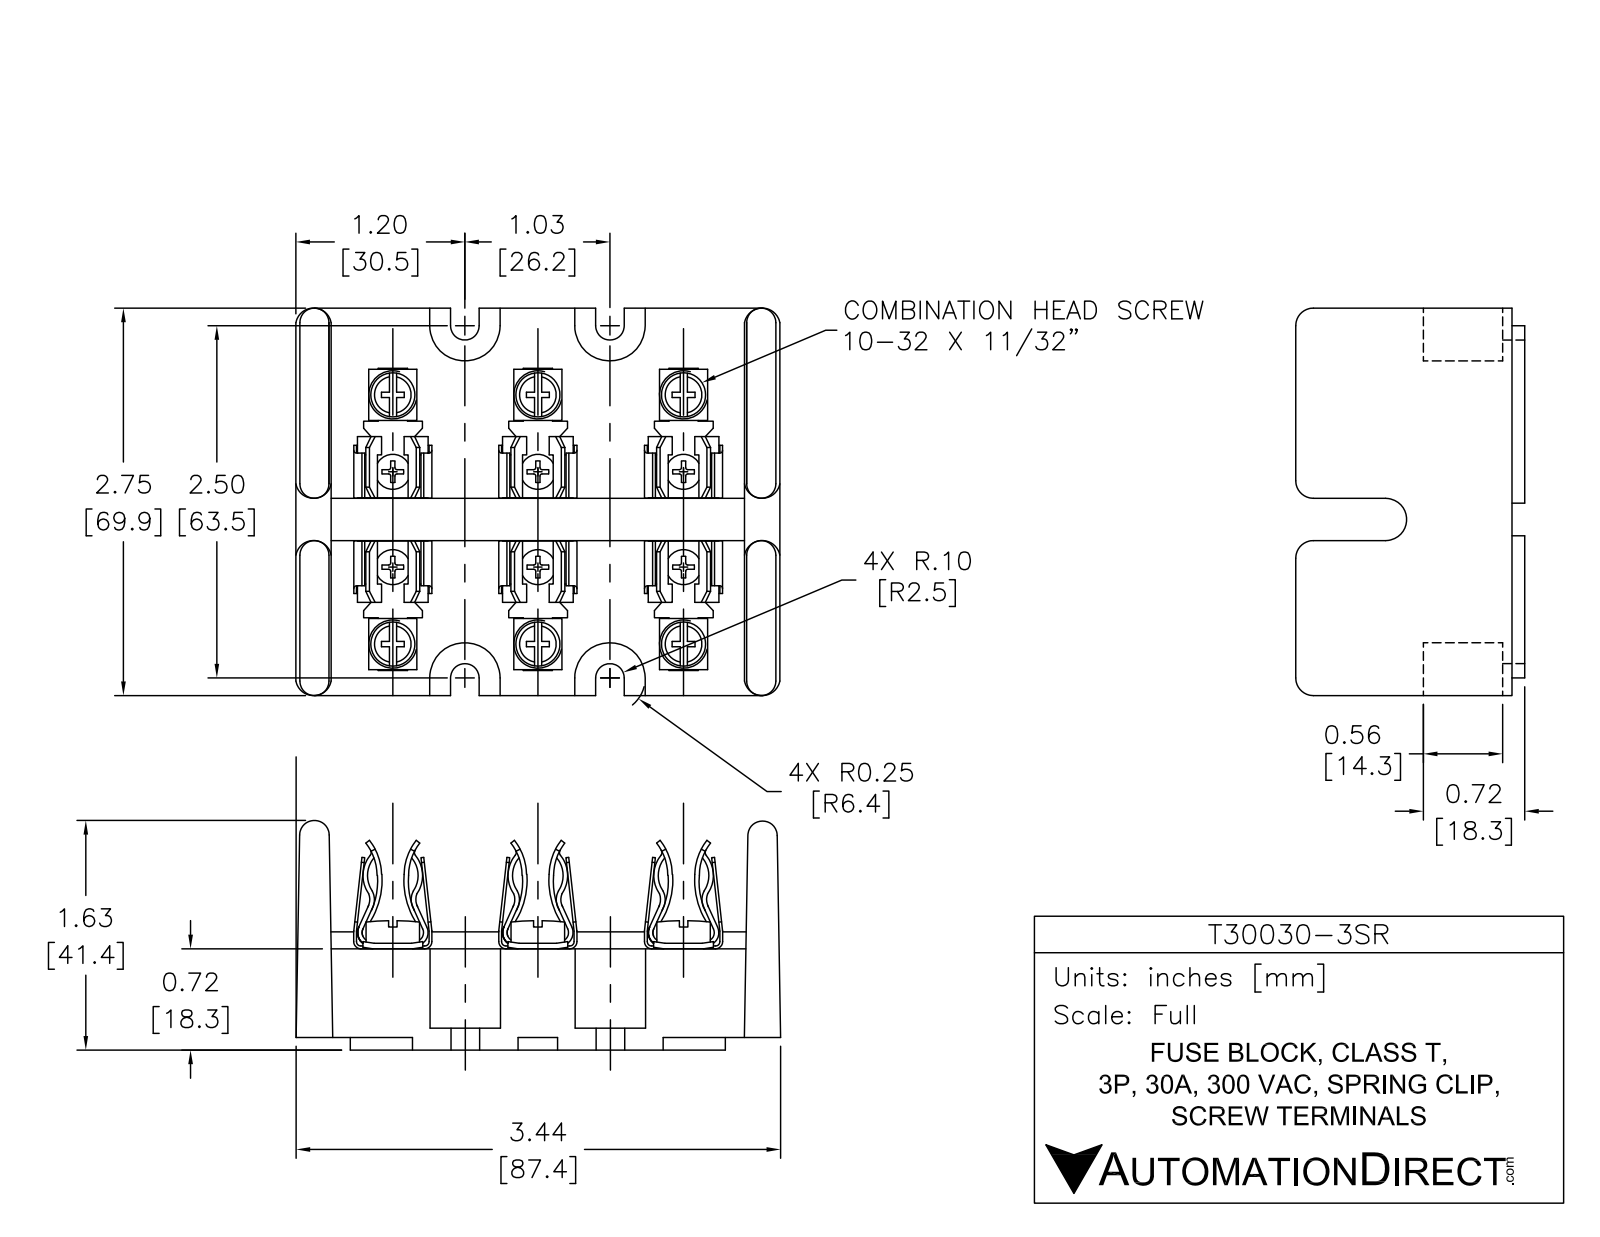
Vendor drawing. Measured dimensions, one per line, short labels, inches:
name: T30030-3SR
written by: SolidWorks 2019 (AUTOMOTIVE_DESIGN)
unit: in
bodies: 13 solids, 586 faces (308 planar, 242 cylindrical, 36 other)
size: 3.441 × 2.75 × 1.63
volume: 7.729 in³; area: 56.51 in²
bosses: 6× ⌀0.375
rounds: 24× R0.2, 12× R0.24, 10× R0.125, 6× R0.205, 6× R0.235, 6× R0.245, 4× R0.1, 4× R0.25
face distances: 0.68, 0.74, 0.06, 0.04, 3.441, 0.25, 3.191, 0.78, 0.72, 2.75
